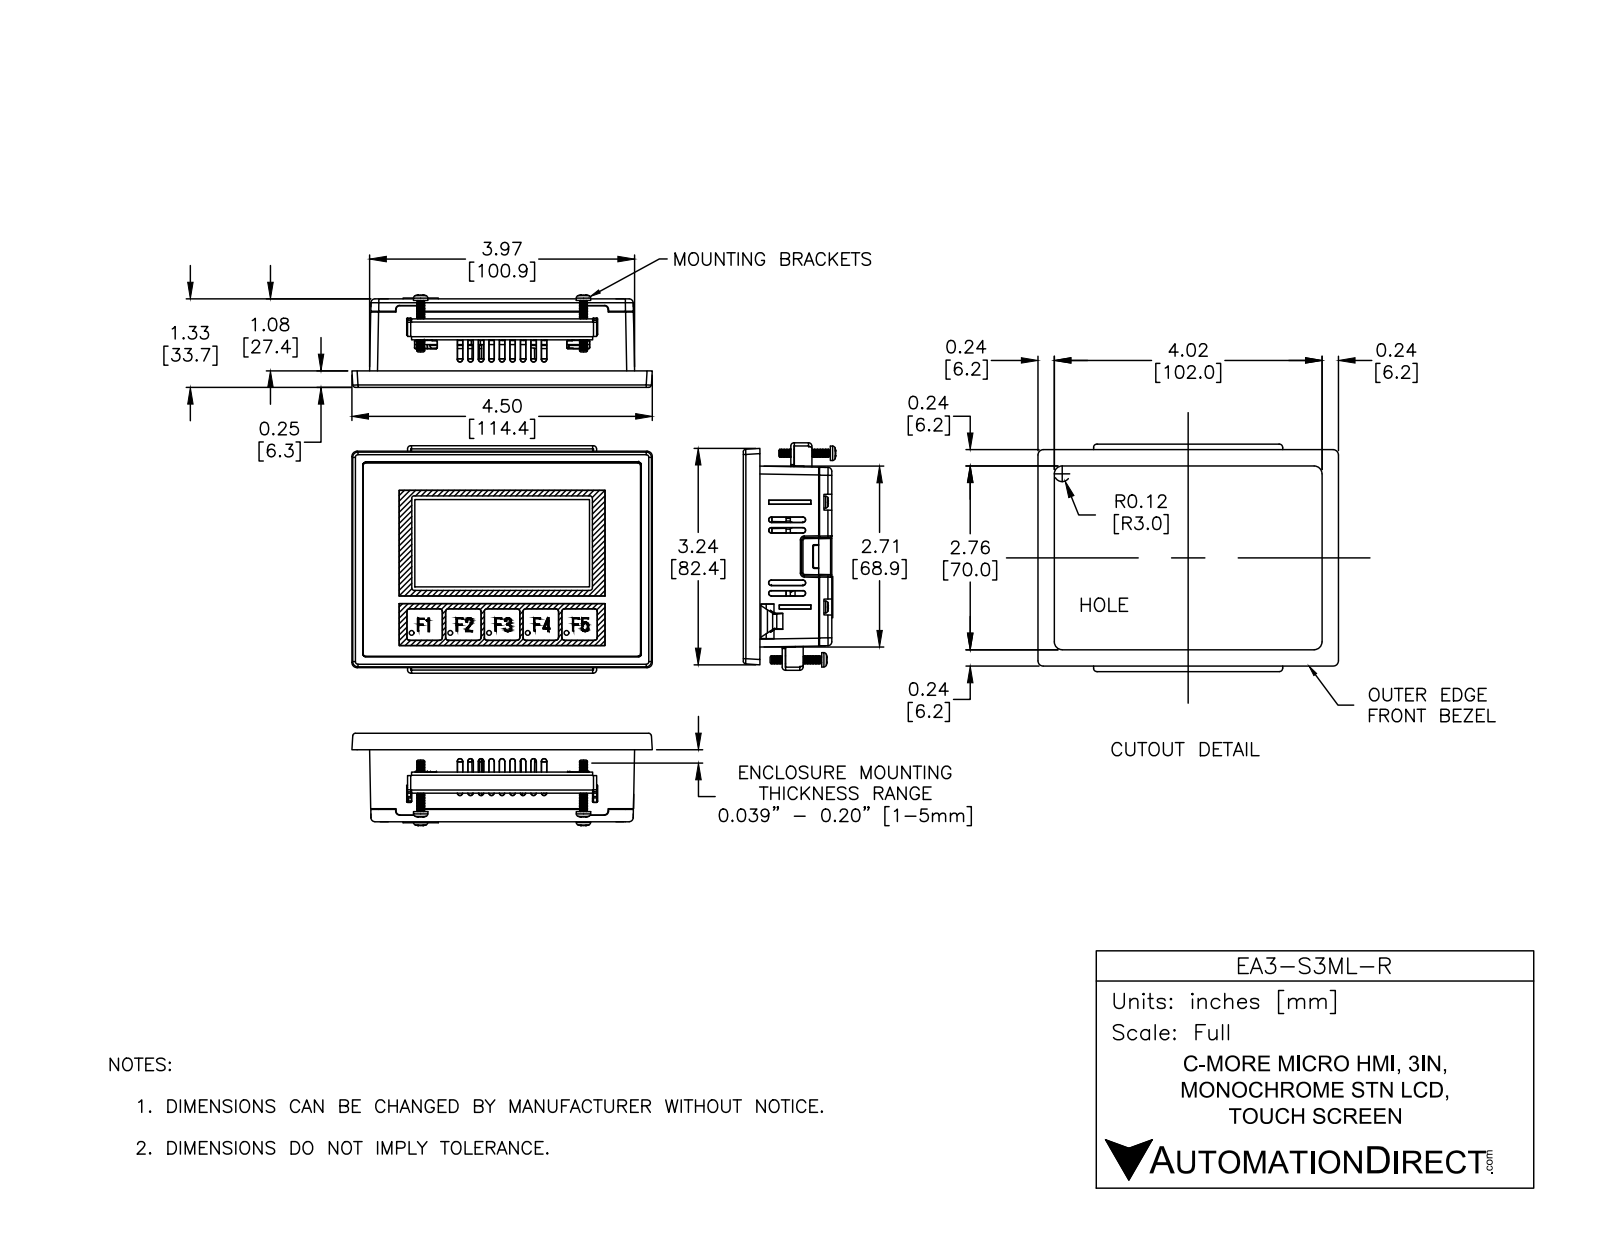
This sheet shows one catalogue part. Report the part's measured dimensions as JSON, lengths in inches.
{"part_name": "EA3-S3ML-R", "step_written_by": "SolidWorks 2017 (AUTOMOTIVE_DESIGN)", "units": "inches", "bodies": {"solids": 1, "faces": 1759, "planar": 1028, "cylindrical": 321, "other": 410}, "overall_size": [4.504, 3.409, 1.386], "volume_in3": 14.72, "surface_area_in2": 73.23, "round_holes": [[0.071, 5], [0.122, 4]], "round_bosses_or_shafts": [[0.217, 4], [0.177, 4], [0.118, 4], [0.087, 4]], "partial_cylinders_radius": [[0.02, 37], [0.039, 30], [0.016, 16], [0.059, 12], [0.118, 10], [0.012, 8], [0.047, 8], [0.066, 4]], "face_to_face_distances": [1.318, 1.313, 0.047, 0.268, 0.315, 1.205, 0.113, 0.108, 0.248, 0.111], "hole_center_spacings": [0.581, 1.161, 1.742, 2.441, 3.095, 3.942, 0.465, 0.512]}
